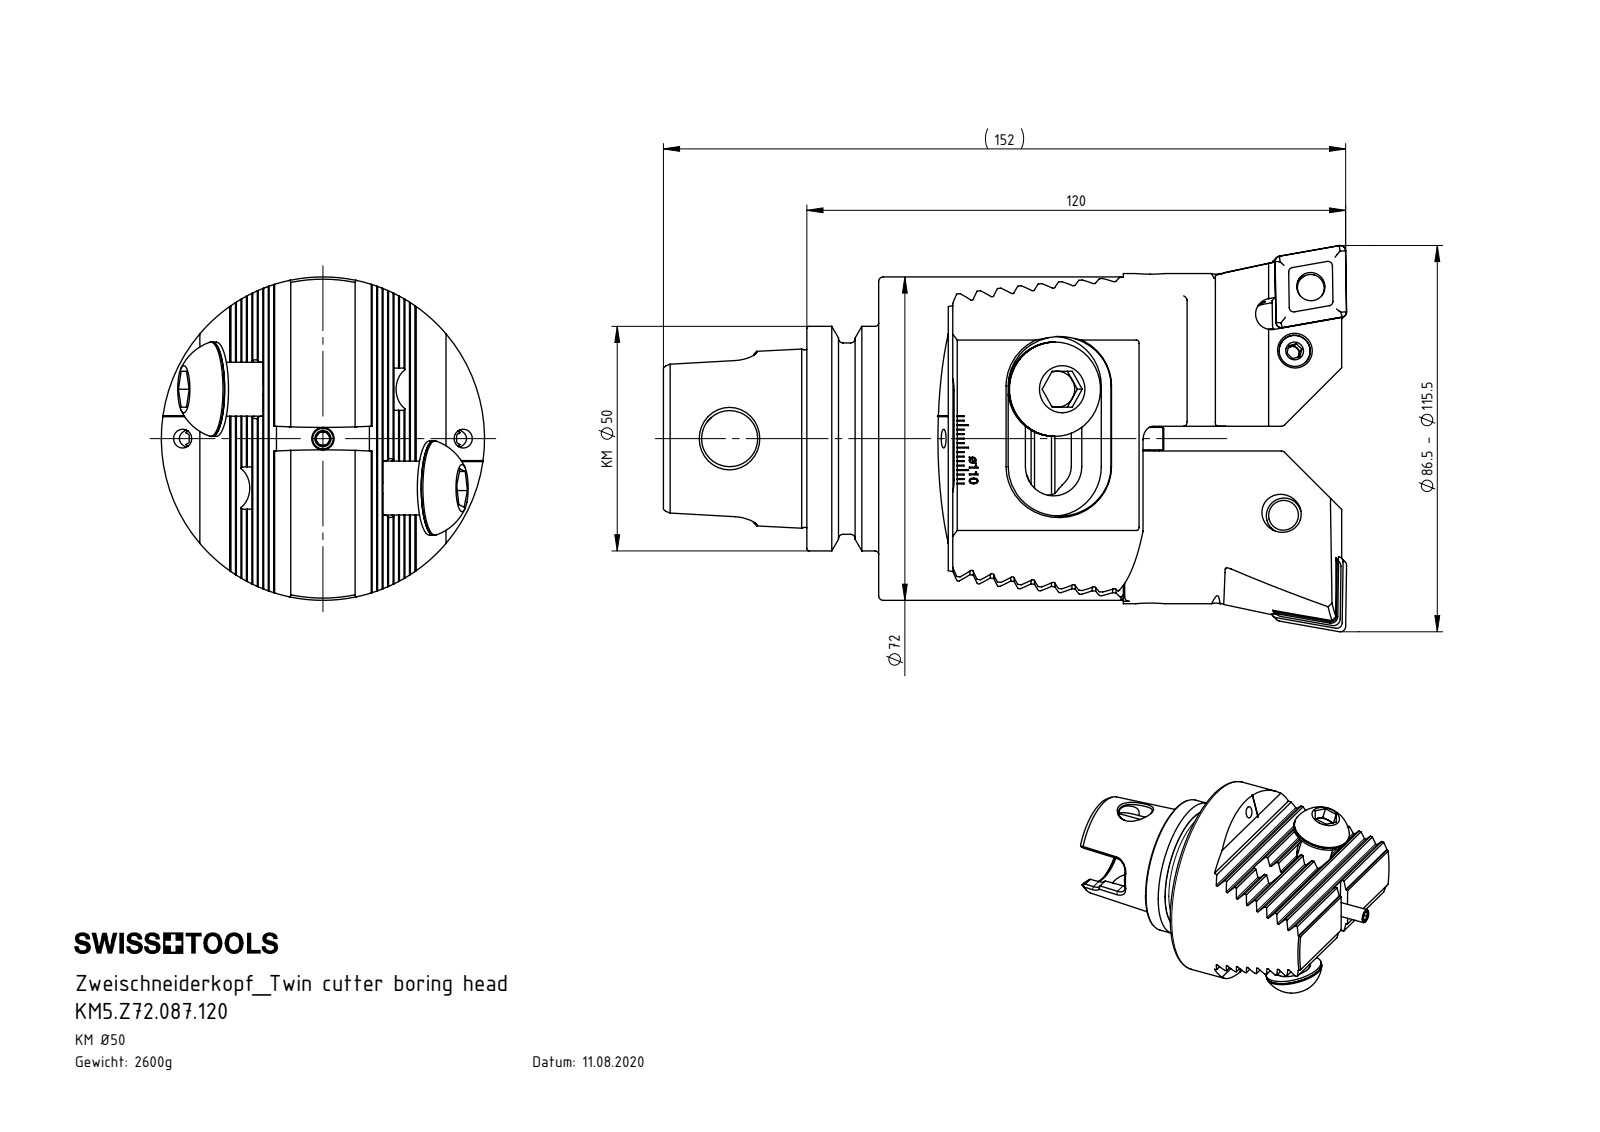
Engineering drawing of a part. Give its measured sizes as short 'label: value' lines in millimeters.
name: KM5.Z72.K23.120; Z72-ER1.003.025_A_gespannt; Z42-ER2.001.019_A; Z72-ER1.001.025 (+2 more)
written by: SolidWorks 2017 (AUTOMOTIVE_DESIGN)
unit: mm
bodies: 6 solids, 309 faces (169 planar, 77 cylindrical, 63 other)
size: 111.45 × 72 × 72
volume: 182 002 mm³; area: 37 742 mm²
holes: 3× ⌀4.2, 2× ⌀10.25, 2× ⌀13, 2× ⌀13.5, 1× ⌀3, 1× ⌀3.3, 1× ⌀6.8, 1× ⌀12.5, 1× ⌀24.5, 1× ⌀28.27, 1× ⌀30
bosses: 2× ⌀21, 2× ⌀12, 1× ⌀72, 1× ⌀50, 1× ⌀42.6, 1× ⌀5, 1× ⌀4, 1× ⌀2.9
rounds: 18× R0.34, 3× R4, 2× R6.04, 2× R220
face distances: 4.07, 8.14, 12.21, 20.36, 16.28, 16.29, 15.5, 24.43, 12.22, 54.5
hole spacings: 40.2
